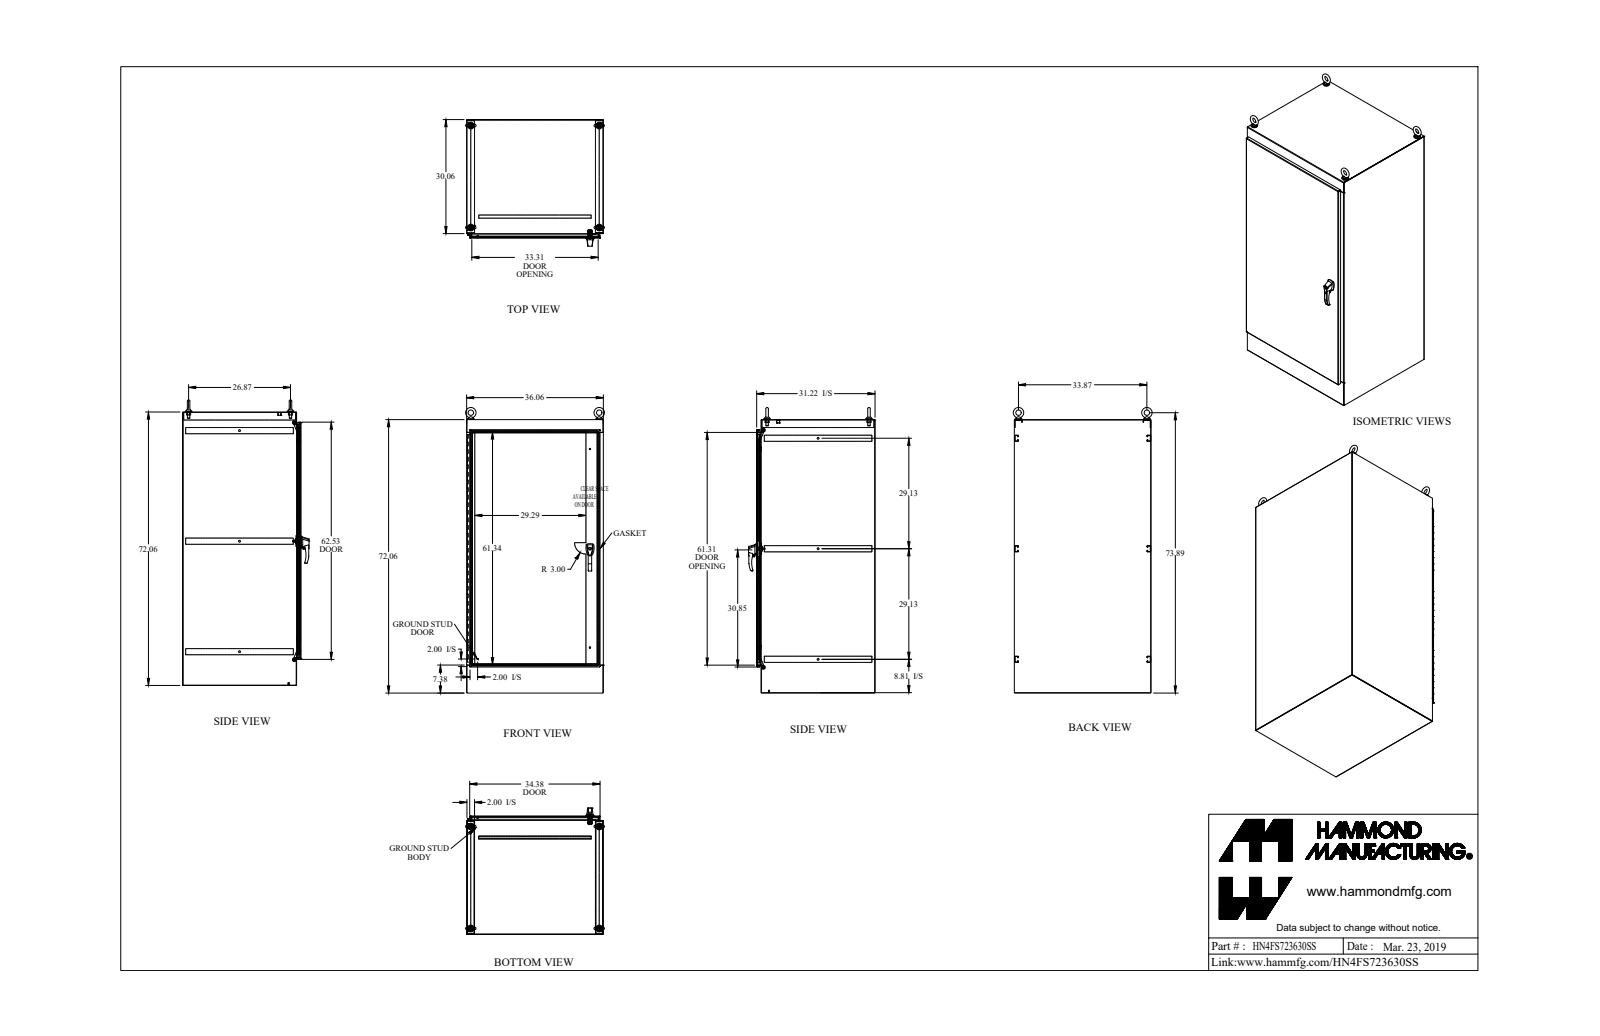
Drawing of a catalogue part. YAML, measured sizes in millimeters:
part_name: "HN4FS723630SS"
step_written_by: "SolidWorks 2018 (AUTOMOTIVE_DESIGN)"
units: millimeters
bodies: {solids: 62, faces: 2004, planar: 899, cylindrical: 880, other: 225}
overall_size: [1917.4, 929.7, 847.4]
volume: 21830000
surface_area: 17980000
round_holes:
  - {diameter: 7.7, count: 10}
  - {diameter: 8.9, count: 7}
  - {diameter: 19.1, count: 6}
  - {diameter: 13.4, count: 4}
  - {diameter: 15.9, count: 4}
  - {diameter: 17.3, count: 4}
  - {diameter: 12.7, count: 3}
  - {diameter: 6.4, count: 2}
  - {diameter: 6.5, count: 2}
  - {diameter: 7.1, count: 2}
  - {diameter: 7.1, count: 2}
  - {diameter: 8, count: 2}
round_bosses_or_shafts:
  - {diameter: 44.5, count: 4}
  - {diameter: 38.1, count: 4}
  - {diameter: 31.8, count: 4}
  - {diameter: 18.7, count: 4}
  - {diameter: 25.4, count: 2}
  - {diameter: 19.1, count: 2}
  - {diameter: 16, count: 2}
  - {diameter: 15.9, count: 2}
partial_cylinders:
  - {radius: 1.1, count: 42}
  - {radius: 3.5, count: 36}
  - {radius: 12.7, count: 23}
  - {radius: 3.2, count: 22}
  - {radius: 0.5, count: 16}
  - {radius: 1.5, count: 15}
  - {radius: 1.2, count: 14}
  - {radius: 3.6, count: 14}
face_to_face_distances: [2.4, 791.3, 913.5, 911.1, 788.8, 1827.9, 915.9, 793.7, 1825.5, 1830.3]
hole_center_spacings: [152.4, 304.8, 457.2, 609.6, 762, 860.3, 914.4, 1066.8]
